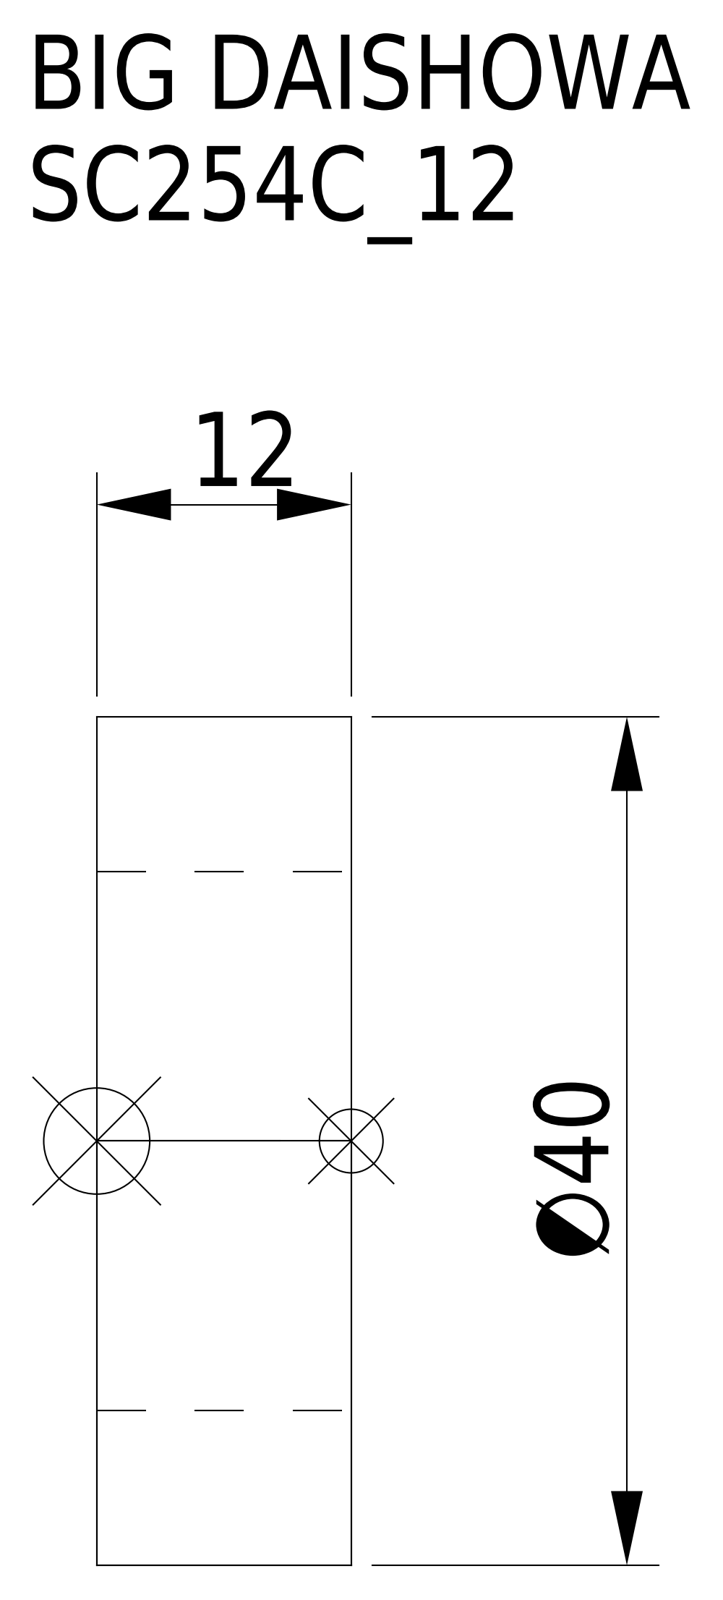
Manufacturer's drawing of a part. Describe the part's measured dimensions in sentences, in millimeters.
The part is named "SC254C_12". Its 3-D file was written by "CREO PARAMETRIC BY PTC INC, 2016380 (AUTOMOTIVE_DESIGN)". It is 1 solid with 8 faces: 5 planar, 3 cylindrical and 0 other. Overall it measures 40 by 40 by 12 millimeters. Its volume is 8 778 cubic millimeters and its surface area 4 003 square millimeters. Round holes: 1 of diameter 25.4. Round bosses or shafts: 1 of diameter 40. The main face-to-face distances are 12, 6.5.
